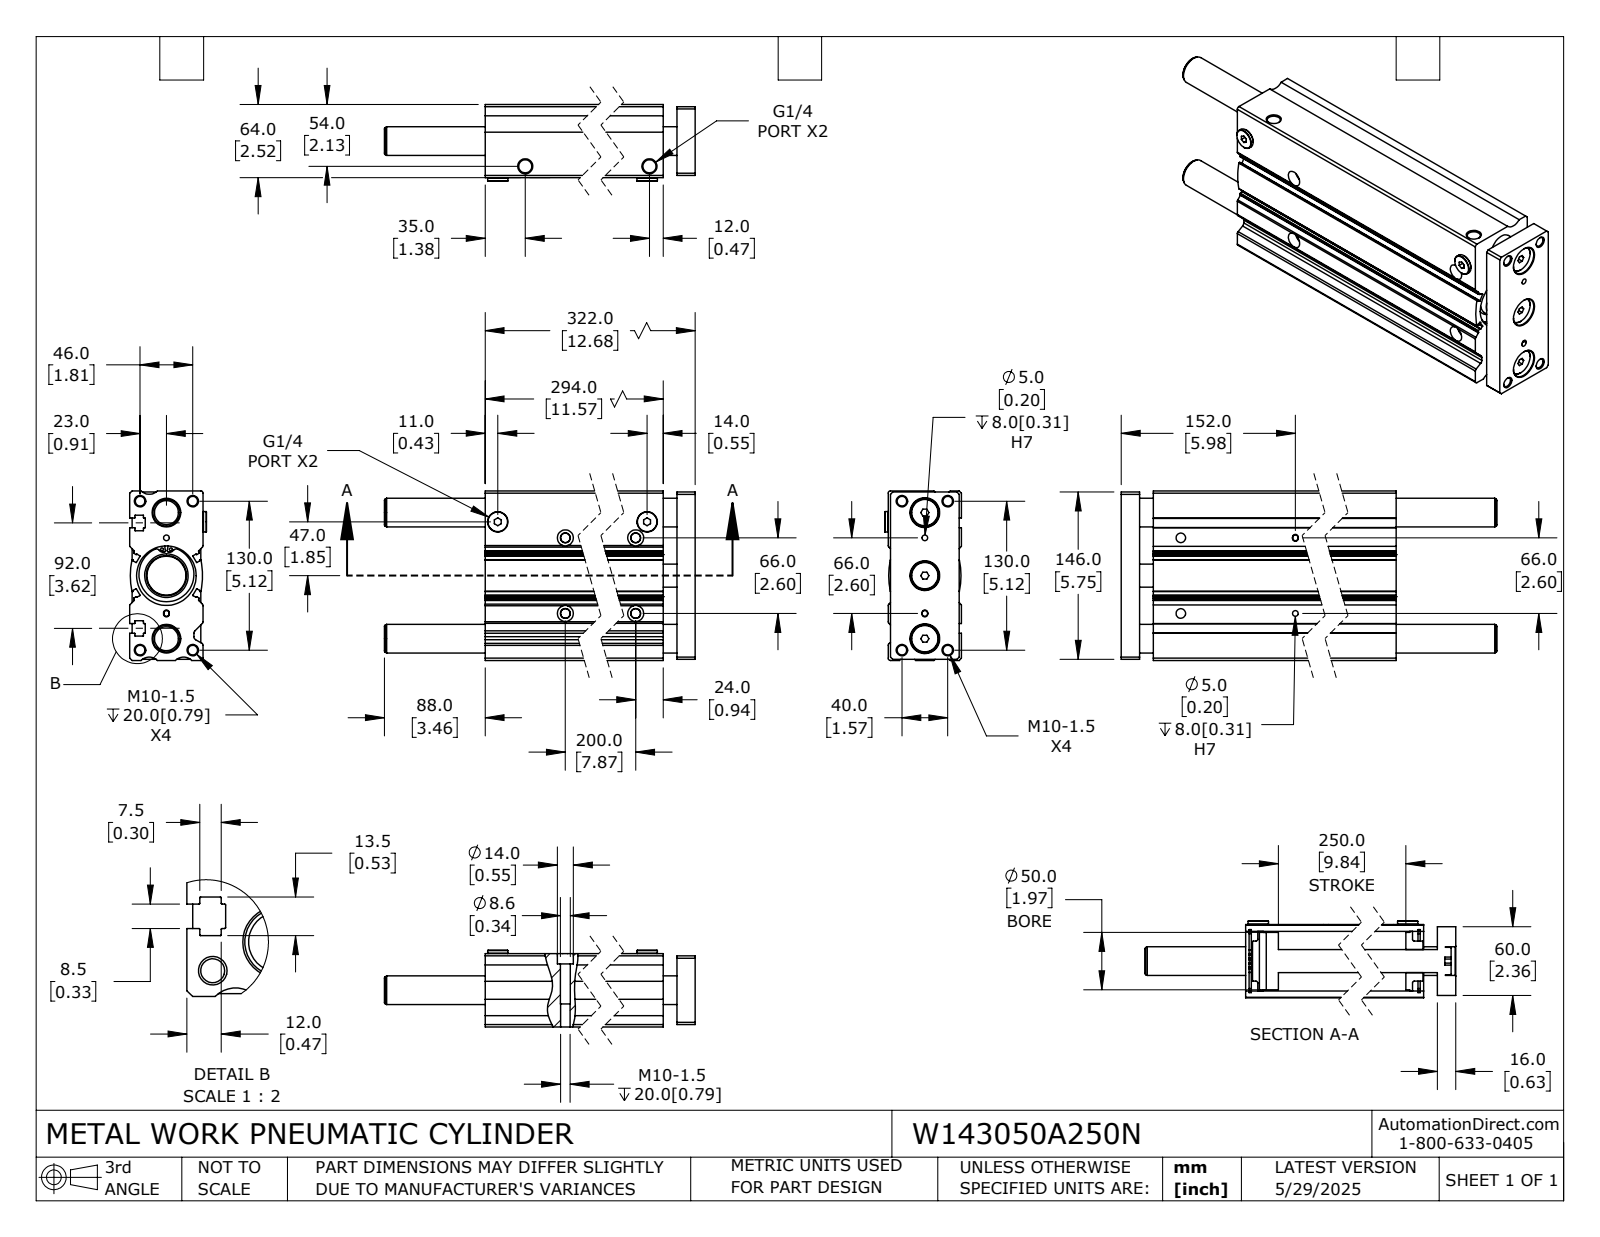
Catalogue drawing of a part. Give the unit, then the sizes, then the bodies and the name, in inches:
Units: inches
Overall size (bounding box): 16.142 × 5.827 × 2.638
Round holes (diameter × count): ⌀0.33 ×12, ⌀0.098 ×4, ⌀0.197 ×4, ⌀0.339 ×4, ⌀0.551 ×4, ⌀0.984 ×3, ⌀0.451 ×2, ⌀1.89 ×2, ⌀0.787 ×1
Round bosses / shafts (diameter × count): ⌀0.945 ×3, ⌀0.697 ×2, ⌀2.165 ×1, ⌀2.047 ×1, ⌀1.969 ×1, ⌀1.378 ×1
Partial cylindrical surfaces — rounded edges, fillets, slot ends (radius × count): R0.012 ×44, R0.02 ×12, R0.118 ×10, R0.079 ×6, R2.677 ×6, R0.039 ×4, R0.098 ×4, R0.394 ×3
Main face-to-face distances: 2.52, 0.472, 5.827, 0.098, 0.531, 11.575, 0.63, 3.622, 0.433, 12.047
Hole centre spacings: 0.118, 0.424, 0.869, 0.88, 0.916, 0.963, 0.987, 1.271
Volume: 139.4 in³ · Surface area: 637 in²
Bodies: 6 solids, 466 faces (186 planar, 224 cylindrical, 56 other)
Part name (STEP PRODUCT): W143050A250N_BODY; W143050A250N; W143050A250N_ROD
STEP written by: SolidWorks 2024 (CONFIG_CONTROL_DESIGN)
